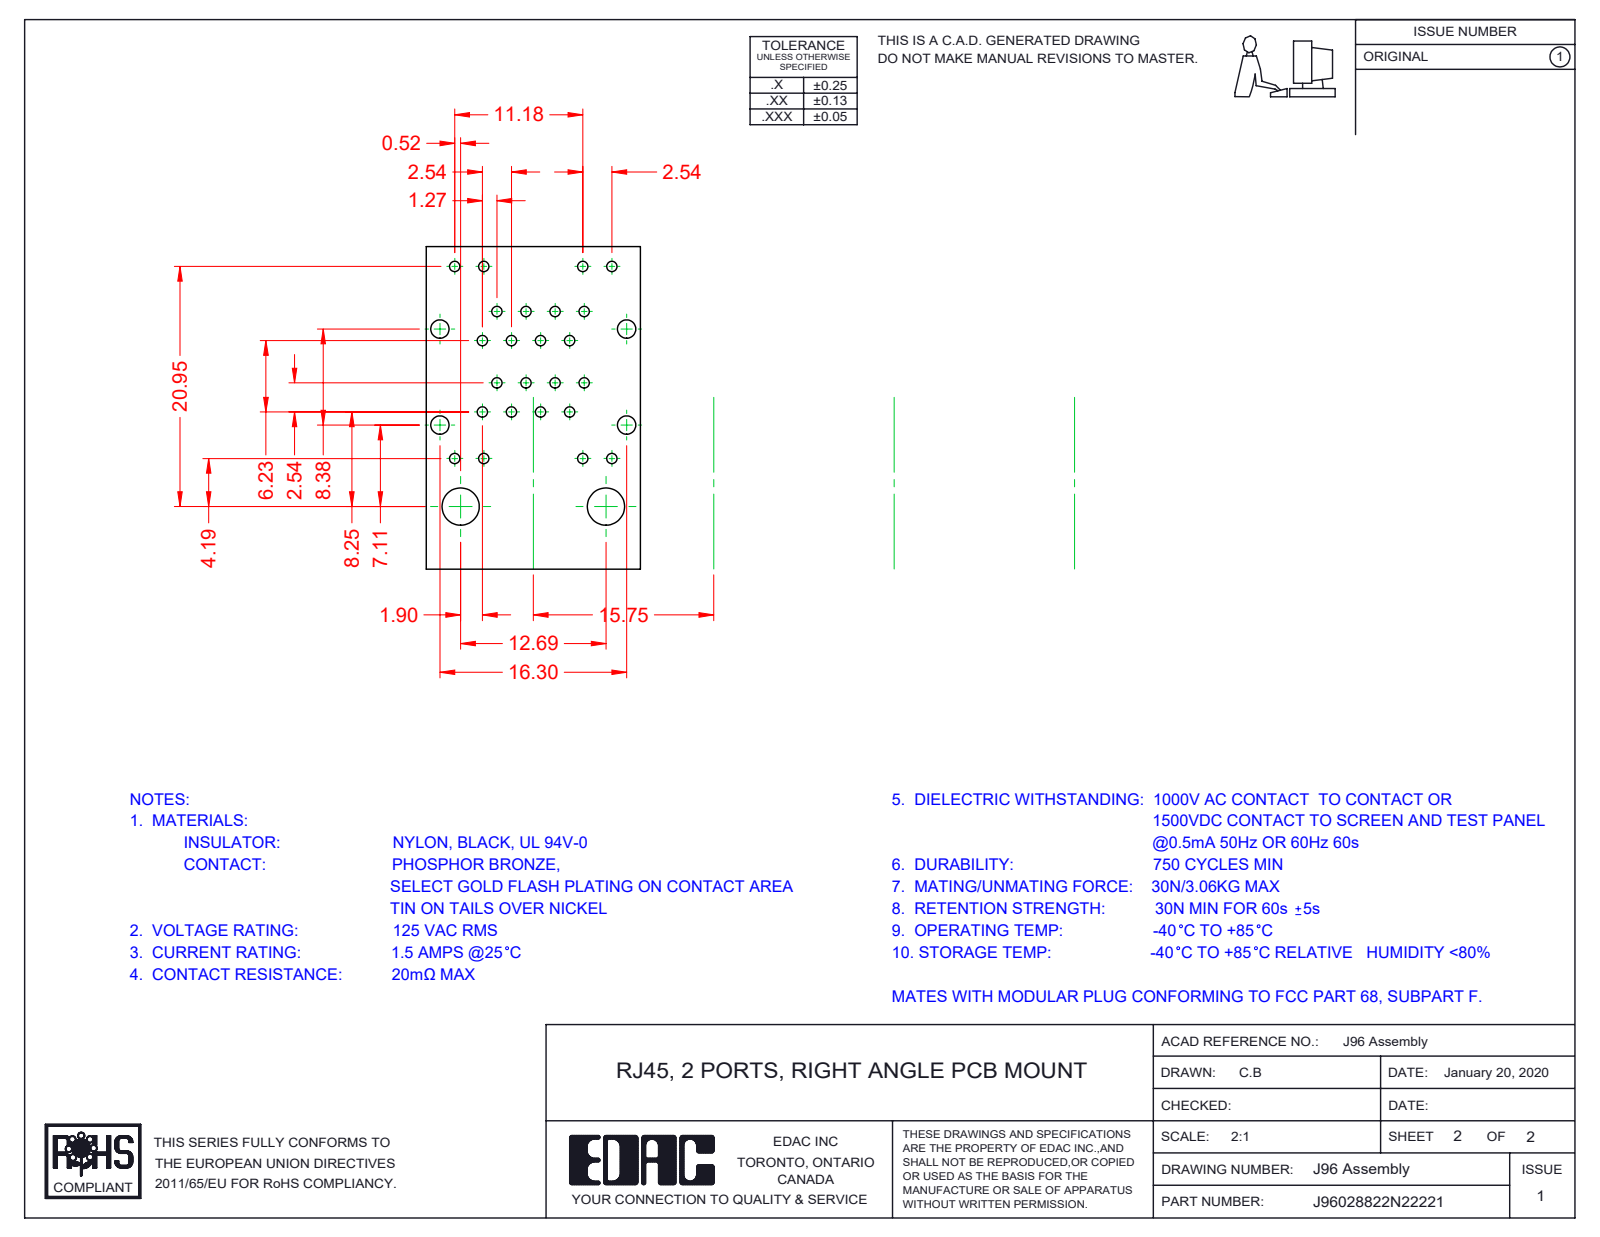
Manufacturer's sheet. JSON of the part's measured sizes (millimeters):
{"part_name": "96 Contacts Lower; 96 LED RH Lower_2-Red; 96 LED LH Lower_2-Red; 96 LED LH Upper_2-Red (+8 more)", "step_written_by": "SolidWorks 2016 (CONFIG_CONTROL_DESIGN)", "units": "millimeters", "bodies": {"solids": 27, "faces": 2417, "planar": 1865, "cylindrical": 446, "other": 106}, "overall_size": [31.38, 28.68, 16.8], "volume_mm3": 6849, "surface_area_mm2": 19094, "partial_cylinders_radius": [[0.25, 48], [0.15, 32], [0.35, 24], [0.5, 16], [1, 16], [0.2, 14], [0.7, 9], [2, 5]], "face_to_face_distances": [16.3, 16.1, 1.75, 16.5, 14.75, 1.55, 14.55, 0.53, 1.48, 11.2]}
